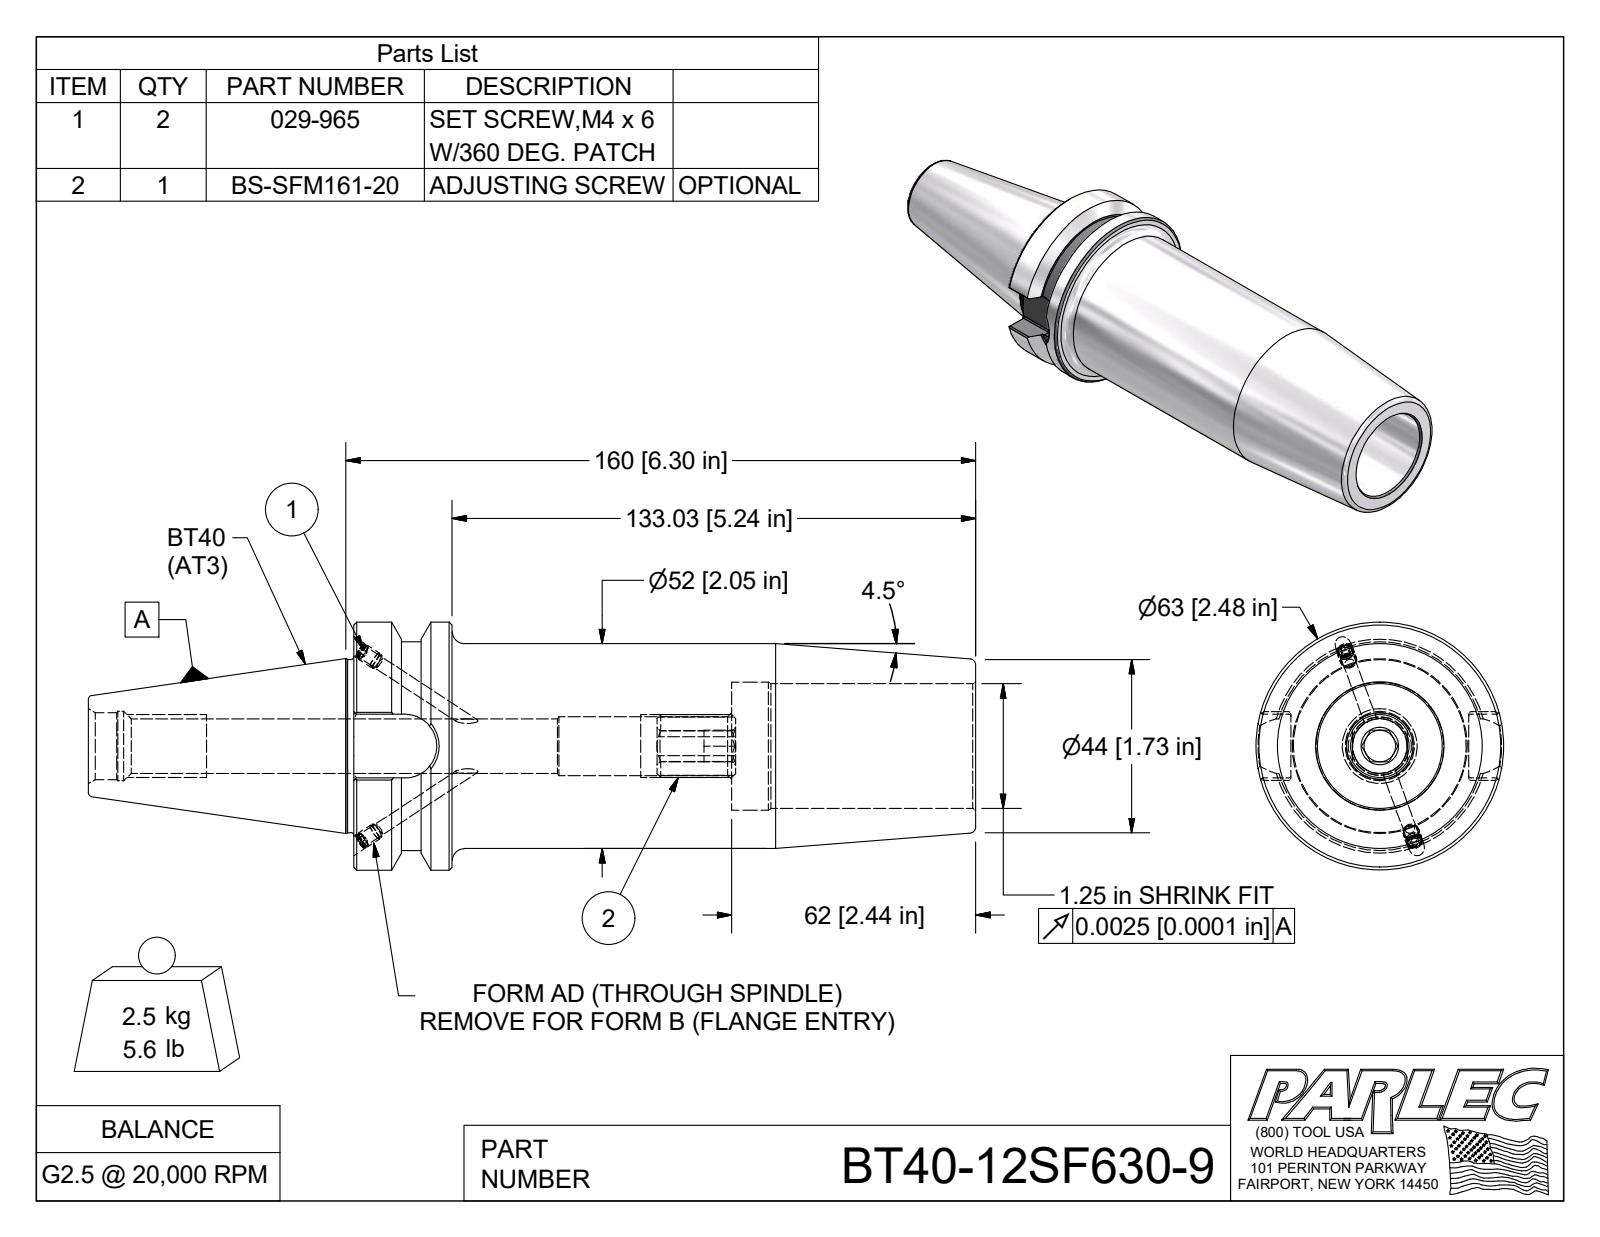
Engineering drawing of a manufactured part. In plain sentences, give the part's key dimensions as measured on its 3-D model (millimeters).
The part is named "BT40-12SF630-9; BT40BC-12SF630-9-1; 029-965; BS-SFM161-20". Its 3-D file was written by "Autodesk Inventor 2009 (AUTOMOTIVE_DESIGN)". It is 4 solids with 131 faces: 57 planar, 33 cylindrical and 41 other. Overall it measures 225.4 by 63 by 63 millimeters. Its volume is 327 600 cubic millimeters and its surface area 54 560 square millimeters. Round holes: 2 of diameter 3.3, 2 of diameter 4.1, 1 of diameter 17.6, 1 of diameter 31.7, 1 of diameter 32.5. Round bosses or shafts: 2 of diameter 4.2, 2 of diameter 4, 1 of diameter 63, 1 of diameter 53, 1 of diameter 52, 1 of diameter 44.5, 1 of diameter 43.9. Partial cylindrical surfaces (rounded edges, fillets, slot ends): 8 of radius 0.5, 1 of radius 8, 1 of radius 8.1. The main face-to-face distances are 96, 158, 62, 25, 71, 133, 15.6, 29.6, 45.2, 67.4.
